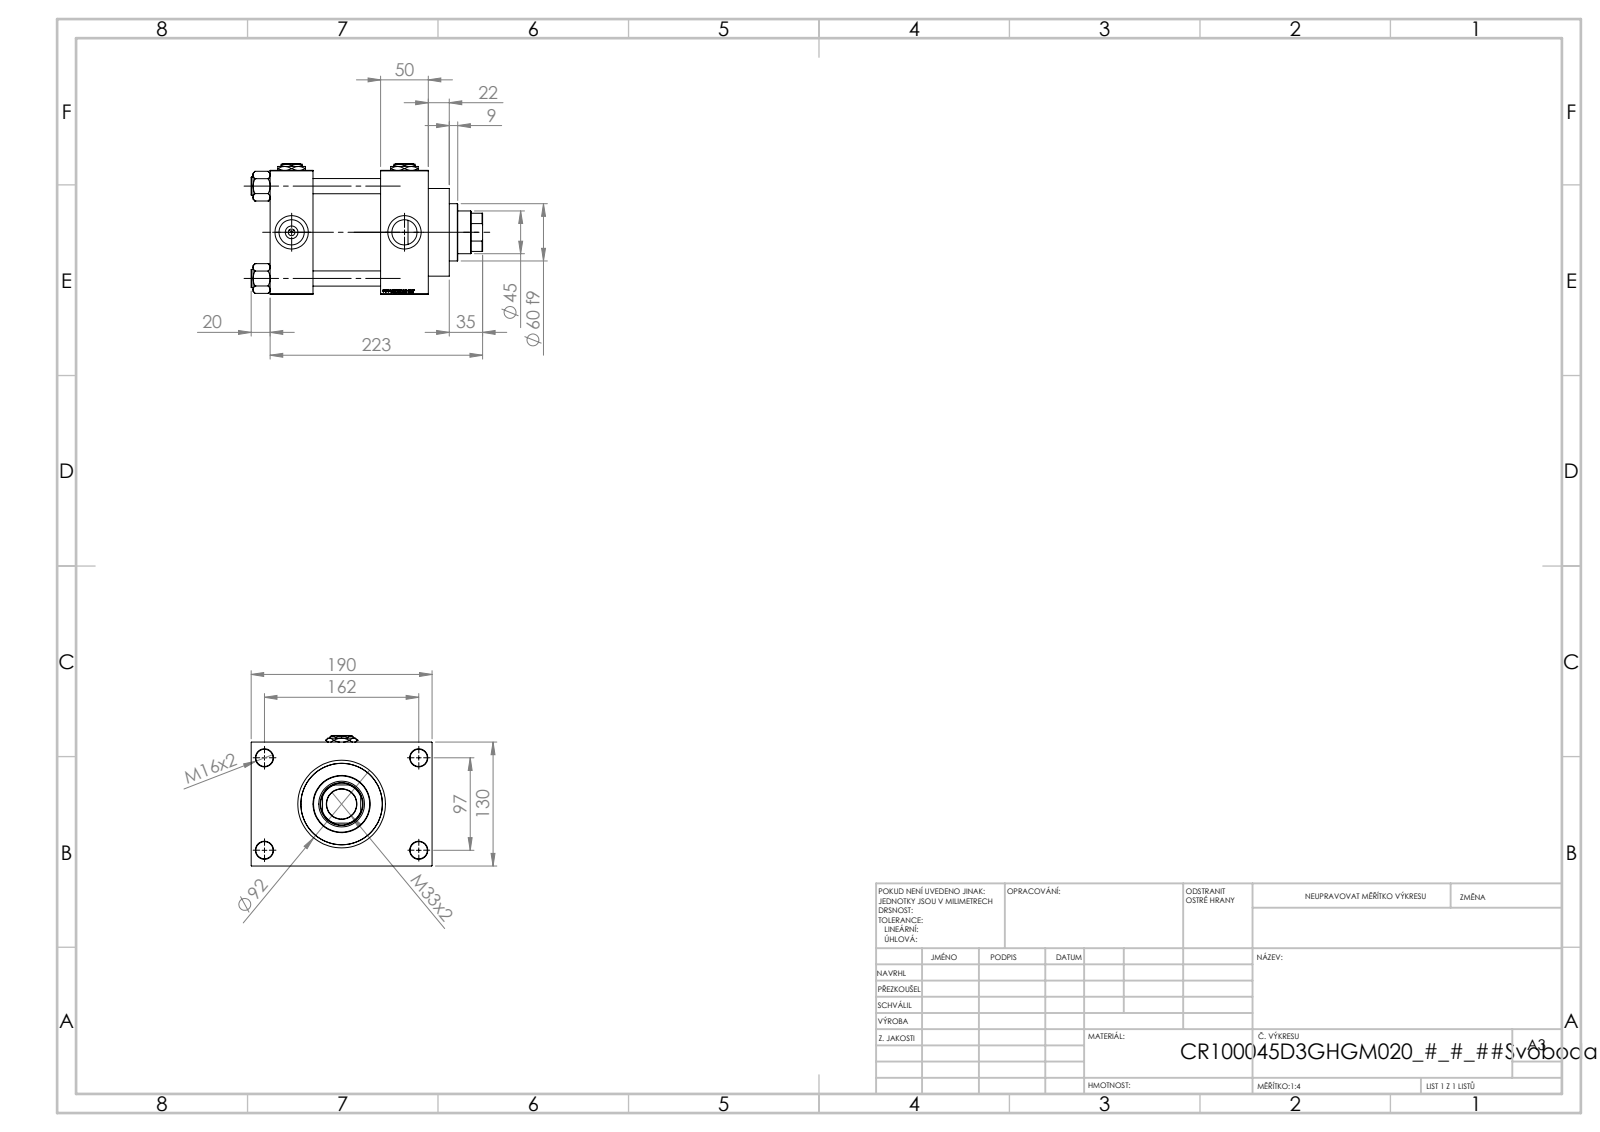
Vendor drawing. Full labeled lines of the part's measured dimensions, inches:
Part name (STEP PRODUCT): V215CR_VCP_D; Zatka_pro_OIL_PORT; V215CR_D_TYCINKA; V215_VC_A (+2 more)
STEP written by: SolidWorks 2019 (CONFIG_CONTROL_DESIGN)
Units: inches
Bodies: 13 solids, 1252 faces (593 planar, 99 cylindrical, 560 other)
Overall size (bounding box): 9.567 × 7.48 × 5.394
Volume: 157.2 in³ · Surface area: 560.8 in²
Round holes (diameter × count): ⌀0.63 ×4, ⌀0.709 ×4, ⌀1.041 ×4, ⌀1.378 ×4, ⌀0.276 ×3, ⌀1.24 ×1, ⌀1.772 ×1, ⌀1.89 ×1, ⌀2.992 ×1, ⌀3.366 ×1, ⌀3.937 ×1
Round bosses / shafts (diameter × count): ⌀0.748 ×4, ⌀4.173 ×1, ⌀3.622 ×1, ⌀2.362 ×1
Partial cylindrical surfaces — rounded edges, fillets, slot ends (radius × count): R0.866 ×1
Main face-to-face distances: 1.772, 5.118, 4.567, 2.795, 6.535, 4.764, 1.969, 1.181, 6.299, 0.787
Hole centre spacings: 1.281, 2.698, 3.717, 3.815, 4.026, 5.096, 6.367, 3.819
